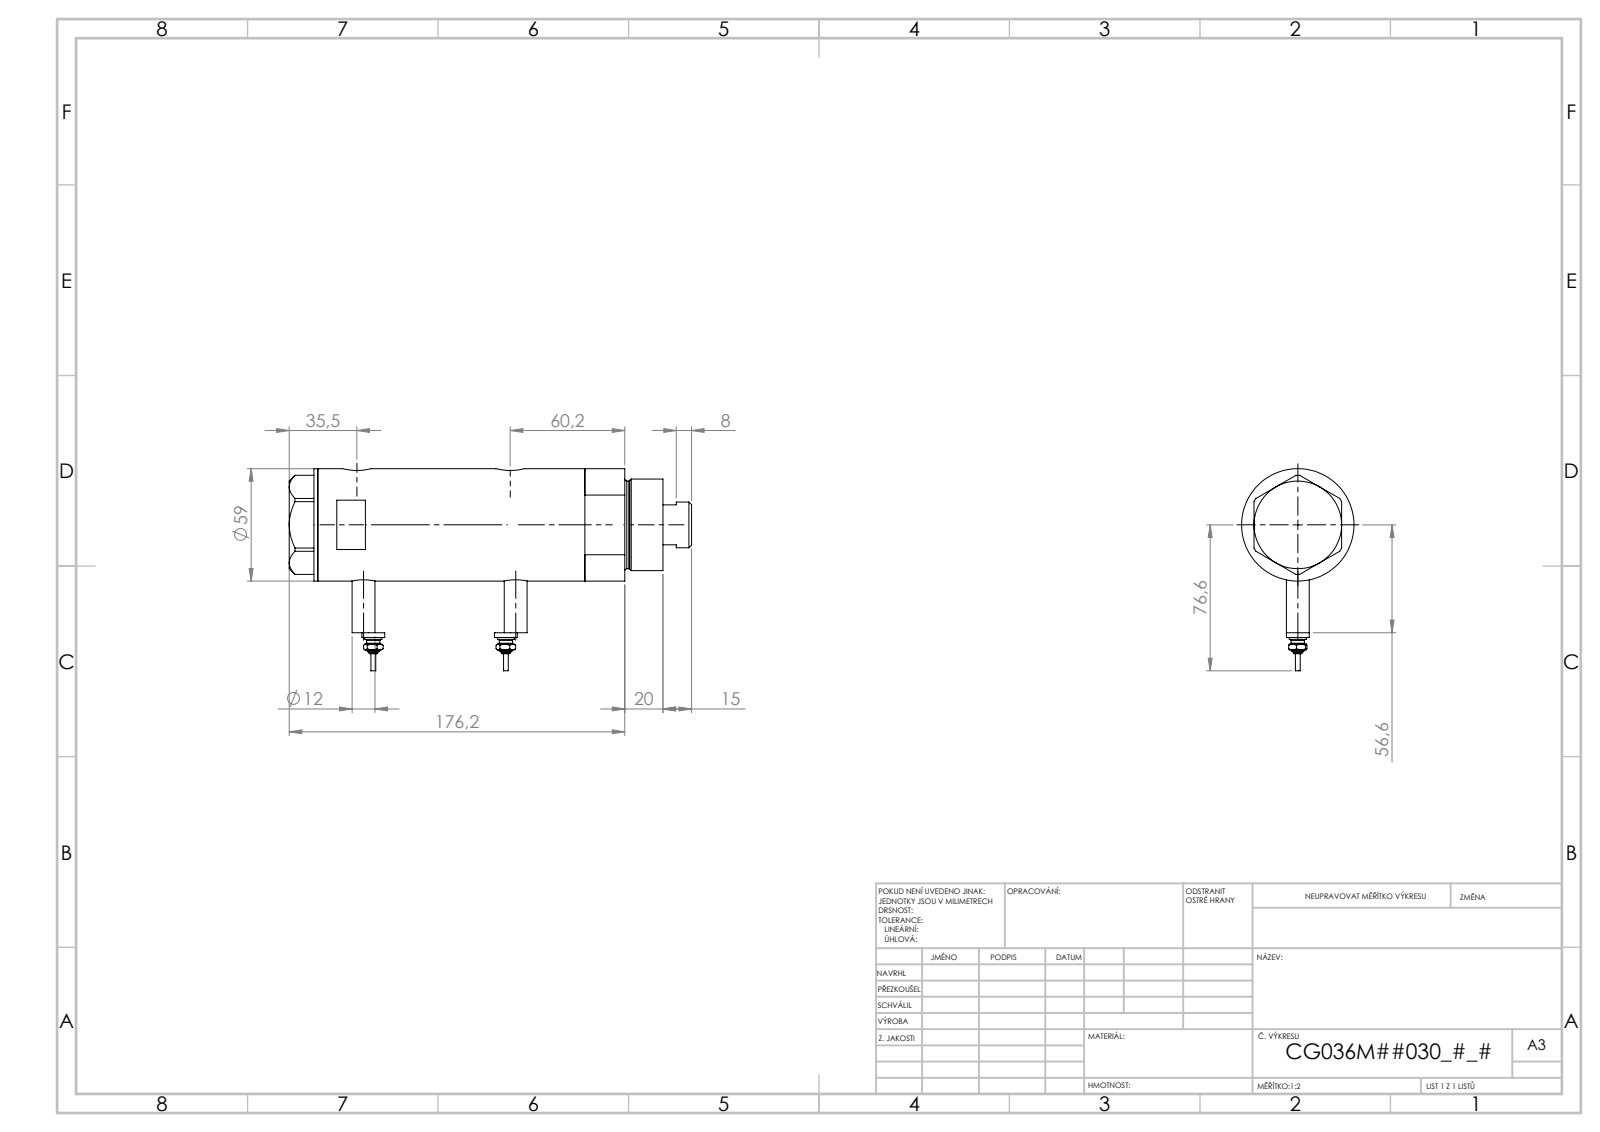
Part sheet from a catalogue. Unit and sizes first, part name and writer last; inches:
Units: inches
Overall size (bounding box): 7.615 × 3.594 × 2.323
Round holes (diameter × count): ⌀0.197 ×2, ⌀0.383 ×2, ⌀0.492 ×2, ⌀0.591 ×2, ⌀0.335 ×1, ⌀0.984 ×1, ⌀1.043 ×1, ⌀1.417 ×1, ⌀1.575 ×1, ⌀2.047 ×1
Round bosses / shafts (diameter × count): ⌀0.472 ×3, ⌀0.354 ×2, ⌀0.276 ×2, ⌀0.171 ×2, ⌀0.094 ×2, ⌀2.323 ×1, ⌀1.89 ×1, ⌀1.811 ×1
Main face-to-face distances: 3.439, 0.925, 2.513, 0.591, 1.516, 4.029, 7.024, 6.434, 5.509, 2.995
Hole centre spacings: 0.114, 0.138, 2.447, 2.561, 2.585, 2.699, 0.114, 0.115
Volume: 26.86 in³ · Surface area: 147.5 in²
Bodies: 6 solids, 232 faces (81 planar, 77 cylindrical, 74 other)
Part name (STEP PRODUCT): V270CG_SWITCH; V270CG_BACK; V270CG_MIDDLE; V270CG_FRONT (+1 more)
STEP written by: SolidWorks 2019 (CONFIG_CONTROL_DESIGN)
